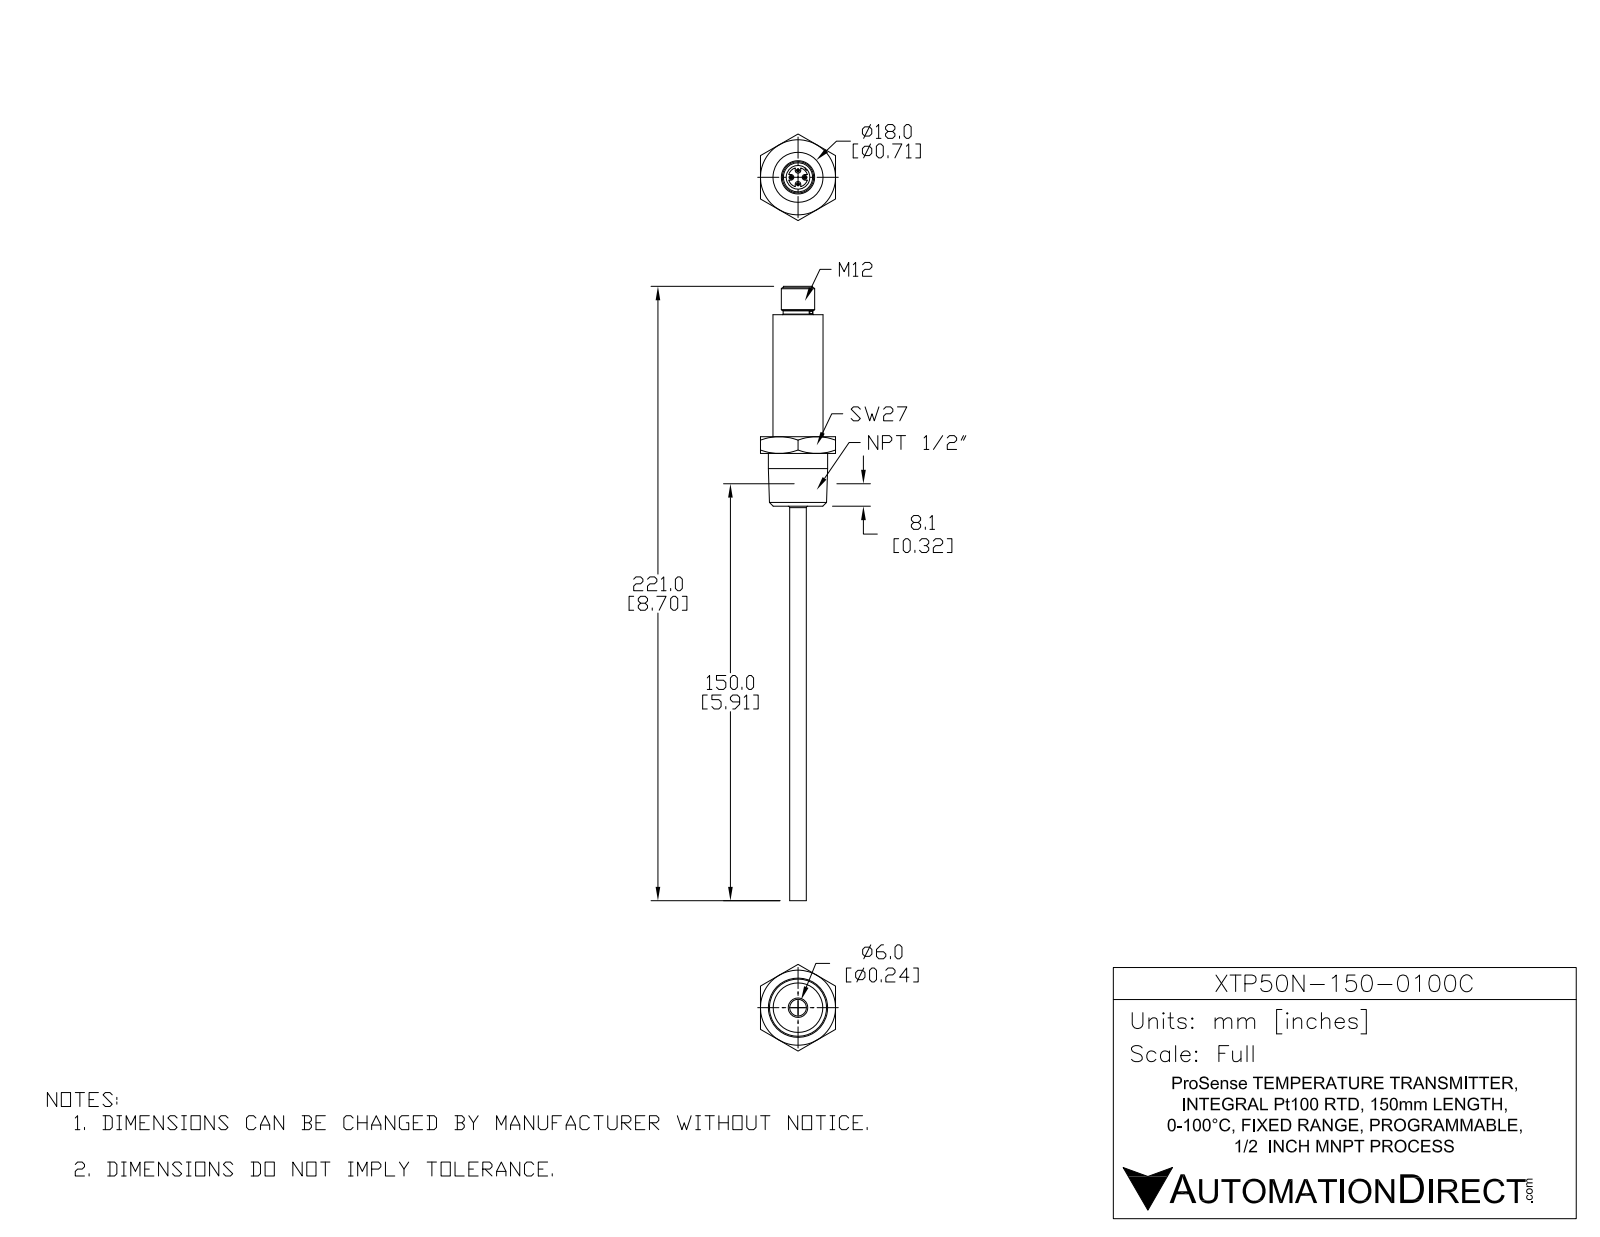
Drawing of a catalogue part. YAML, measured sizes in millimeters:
part_name: "XTP50N-150-0100C"
step_written_by: "SolidWorks 2015 (AUTOMOTIVE_DESIGN)"
units: millimeters
bodies: {solids: 1, faces: 117, planar: 43, cylindrical: 34, other: 40}
overall_size: [221, 31.18, 27]
volume: 25748
surface_area: 9159
round_holes:
  - {diameter: 4, count: 1}
  - {diameter: 8.5, count: 1}
round_bosses_or_shafts:
  - {diameter: 1.02, count: 4}
  - {diameter: 21.34, count: 1}
  - {diameter: 18, count: 1}
  - {diameter: 12, count: 1}
  - {diameter: 10.7, count: 1}
  - {diameter: 10.5, count: 1}
  - {diameter: 6, count: 1}
partial_cylinders:
  - {radius: 1, count: 4}
  - {radius: 3.5, count: 1}
  - {radius: 4.25, count: 1}
face_to_face_distances: [27, 25, 19, 6, 68.9, 49.9, 43.9, 79.1, 60.1, 54.1]
